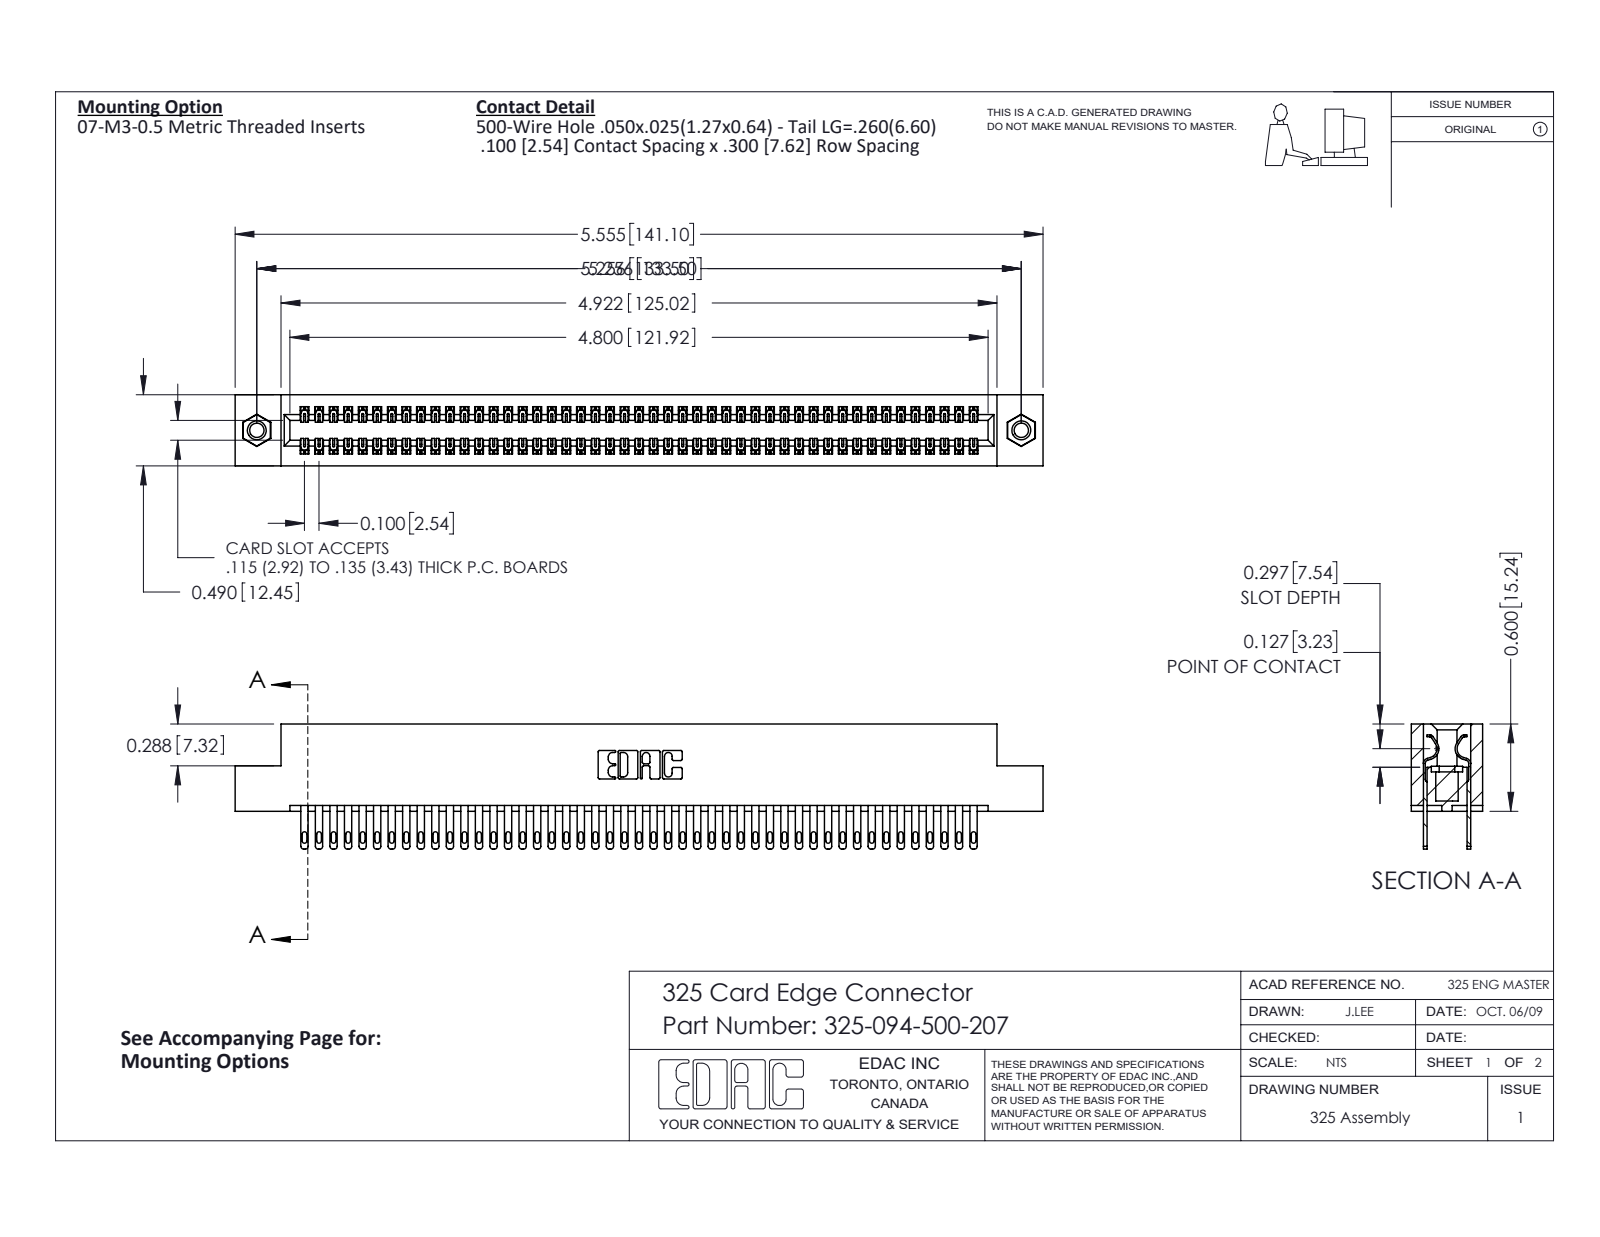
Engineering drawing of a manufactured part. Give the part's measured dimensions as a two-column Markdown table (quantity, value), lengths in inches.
| quantity | value |
| --- | --- |
| part name | 325 Part_TI; 345-250-001_345-250-005-103; 325-292-001_325-293-100; 325-094-500-207 |
| STEP written by | SolidWorks 2016 (CONFIG_CONTROL_DESIGN) |
| units | inches |
| bodies | 97 solids, 4686 faces (2922 planar, 1748 cylindrical, 16 other) |
| overall size | 5.555 × 0.86 × 0.49 |
| volume | 1.131 in³ |
| surface area | 36.52 in² |
| round holes (diameter × count) | 0.098 × 2, 0.125 × 2, 0.16 × 2 |
| round bosses / shafts (diameter × count) | 0.155 × 2 |
| partial cylindrical surfaces (radius × count) | 0.006 × 141, 0.016 × 94, 0.02 × 94, 0.01 × 22, 0.007 × 6, 0.031 × 6, 0.026 × 3, 0.014 × 2 |
| main face-to-face distances | 0.083, 0.407, 0.3, 0.107, 0.383, 0.025, 0.49, 0.325, 0.275, 0.56 |
| hole center spacings | 5.256 |
